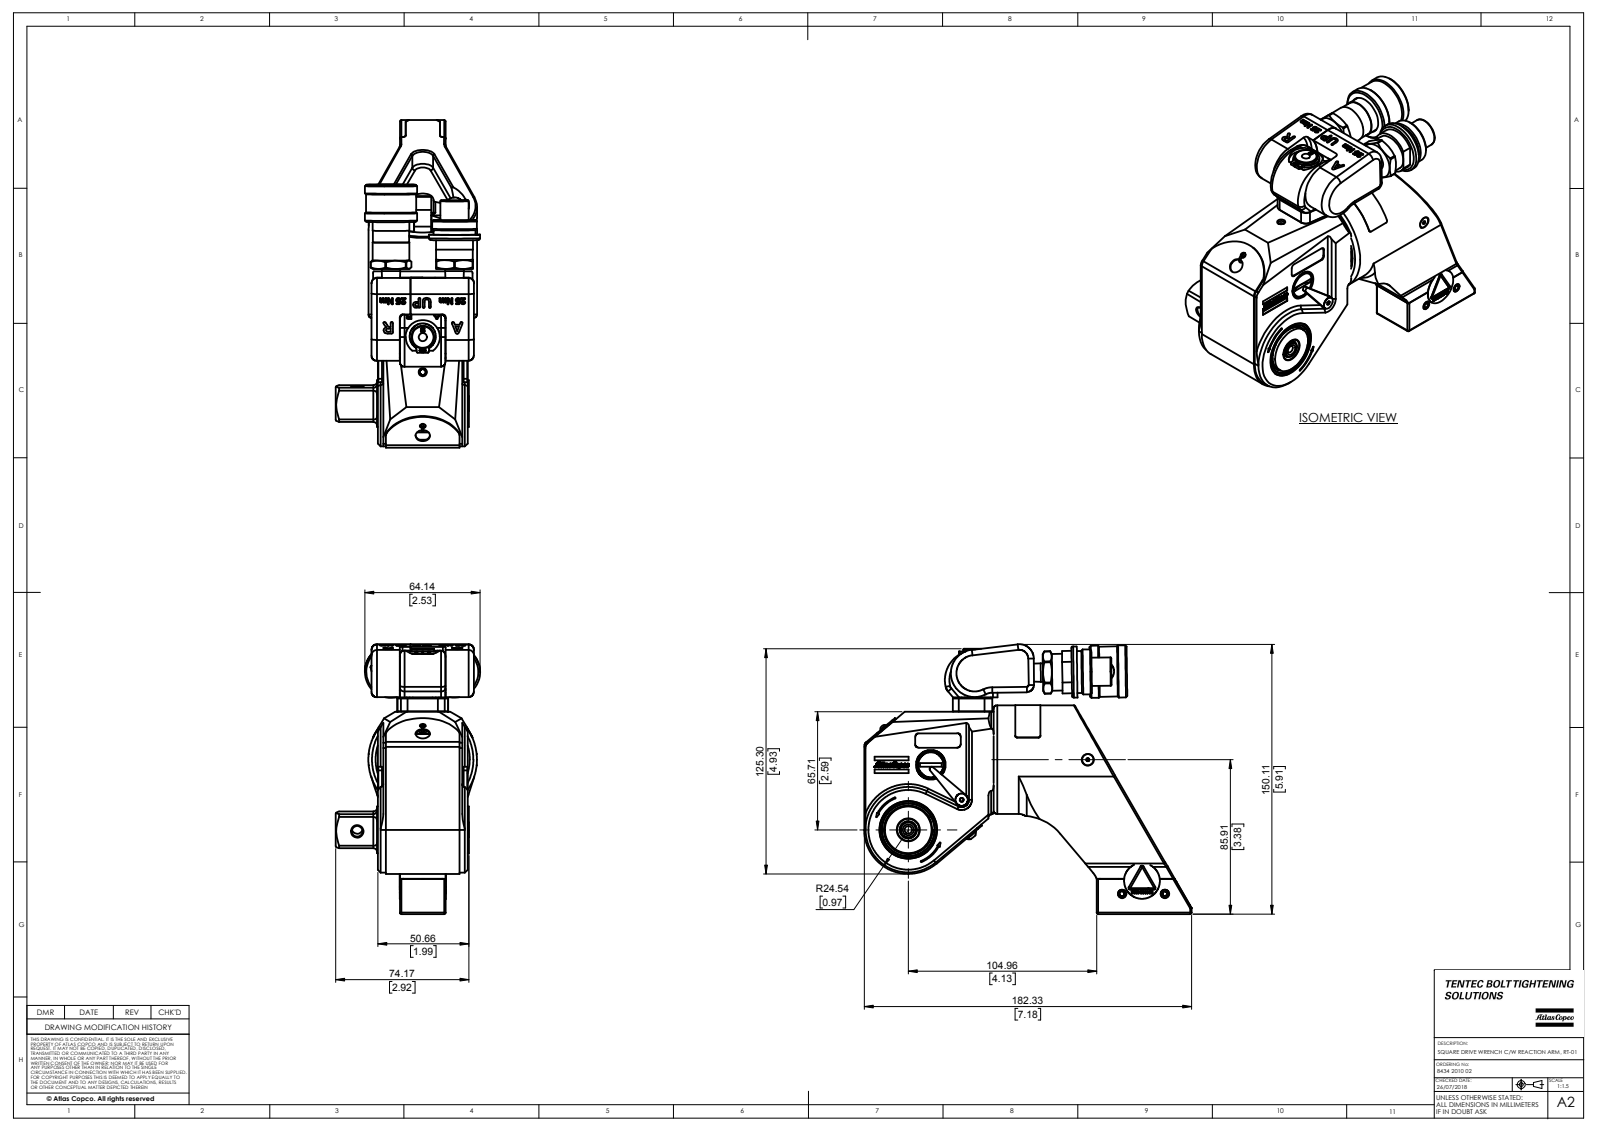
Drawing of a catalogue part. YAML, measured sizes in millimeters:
part_name: "RT-01_8434 2010 02"
step_written_by: "SolidWorks 2017 (CONFIG_CONTROL_DESIGN)"
units: millimeters
bodies: {solids: 1, faces: 1081, planar: 409, cylindrical: 337, other: 335}
overall_size: [182.33, 150.06, 79.16]
volume: 607176
surface_area: 86746
round_holes:
  - {diameter: 3.5, count: 4}
  - {diameter: 2.72, count: 2}
  - {diameter: 6, count: 1}
  - {diameter: 6.38, count: 1}
  - {diameter: 14.25, count: 1}
  - {diameter: 14.5, count: 1}
  - {diameter: 17, count: 1}
  - {diameter: 18.39, count: 1}
  - {diameter: 46.84, count: 1}
  - {diameter: 51.59, count: 1}
round_bosses_or_shafts:
  - {diameter: 20.45, count: 2}
  - {diameter: 10.3, count: 2}
  - {diameter: 6.65, count: 2}
  - {diameter: 4.75, count: 2}
  - {diameter: 60.45, count: 1}
  - {diameter: 45.72, count: 1}
  - {diameter: 29.05, count: 1}
  - {diameter: 28.5, count: 1}
partial_cylinders:
  - {radius: 1.5, count: 11}
  - {radius: 0.79, count: 10}
  - {radius: 1.6, count: 10}
  - {radius: 2, count: 9}
  - {radius: 2.5, count: 8}
  - {radius: 3, count: 7}
  - {radius: 0.8, count: 6}
  - {radius: 3.81, count: 5}
face_to_face_distances: [47.02, 3.02, 50.04, 34.7, 12.32, 37.72, 9.3, 44, 1.9, 4.92]
hole_center_spacings: [14.54, 23.66, 16.86, 20.68, 23.83, 52.94, 70.82, 103.51]
